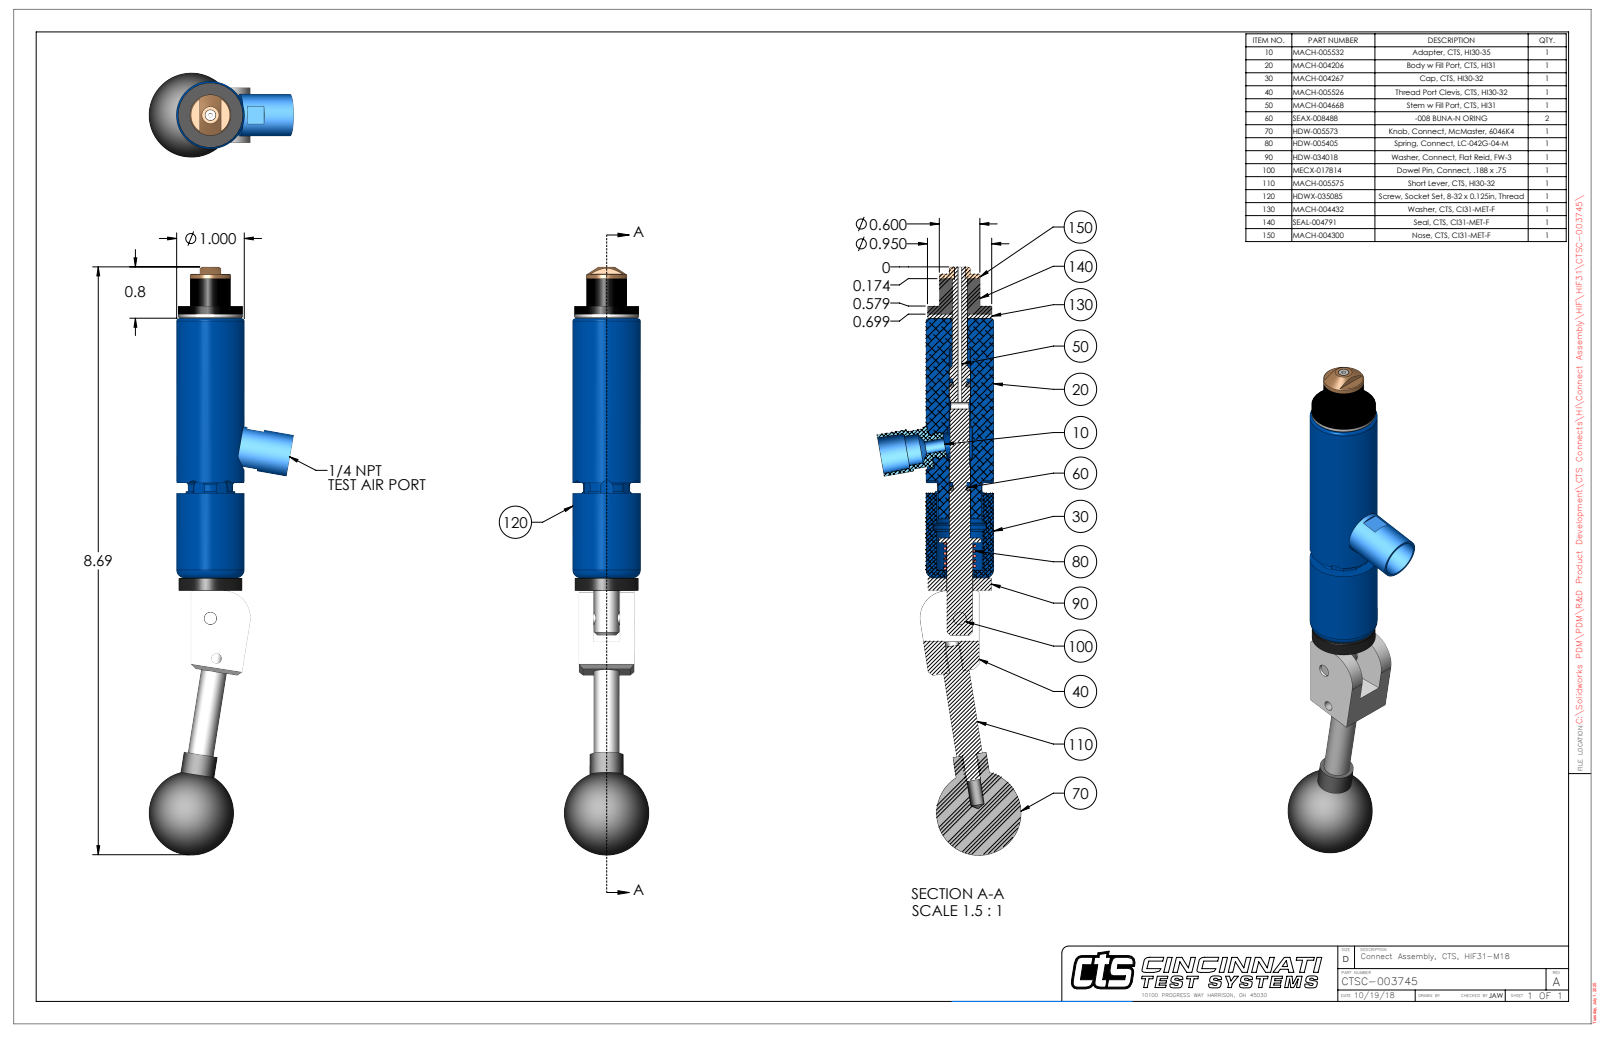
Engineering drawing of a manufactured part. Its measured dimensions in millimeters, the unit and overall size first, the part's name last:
Units: millimetres
Overall size (bounding box): 220.8 × 54.1 × 31.8
Round holes (diameter × count): ⌀5.1 ×2, ⌀1.6 ×1, ⌀2.8 ×1, ⌀3.5 ×1, ⌀3.8 ×1, ⌀4 ×1, ⌀4.7 ×1, ⌀4.8 ×1, ⌀5.5 ×1, ⌀5.8 ×1, ⌀5.8 ×1, ⌀9.8 ×1
Round bosses / shafts (diameter × count): ⌀25.4 ×1, ⌀24.1 ×1, ⌀23.8 ×1, ⌀15.7 ×1, ⌀15.2 ×1, ⌀12.7 ×1, ⌀9.7 ×1, ⌀9.5 ×1
Partial cylindrical surfaces — rounded edges, fillets, slot ends (radius × count): R2.4 ×6, R0.7 ×2, R1.7 ×1, R8.3 ×1, R9.5 ×1, R10.2 ×1, R11.5 ×1
Main face-to-face distances: 1.5, 5.3, 15.3, 99, 97.4, 20.6, 103.7, 102.2, 4.7, 9.9
Hole centre spacings: 15.2, 42.1, 57.2
Volume: 85 560 mm³ · Surface area: 26 570 mm²
Bodies: 9 solids, 302 faces (115 planar, 122 cylindrical, 65 other)
Part name (STEP PRODUCT): CTSC-003745
STEP written by: SolidWorks 2023 (AUTOMOTIVE_DESIGN)
